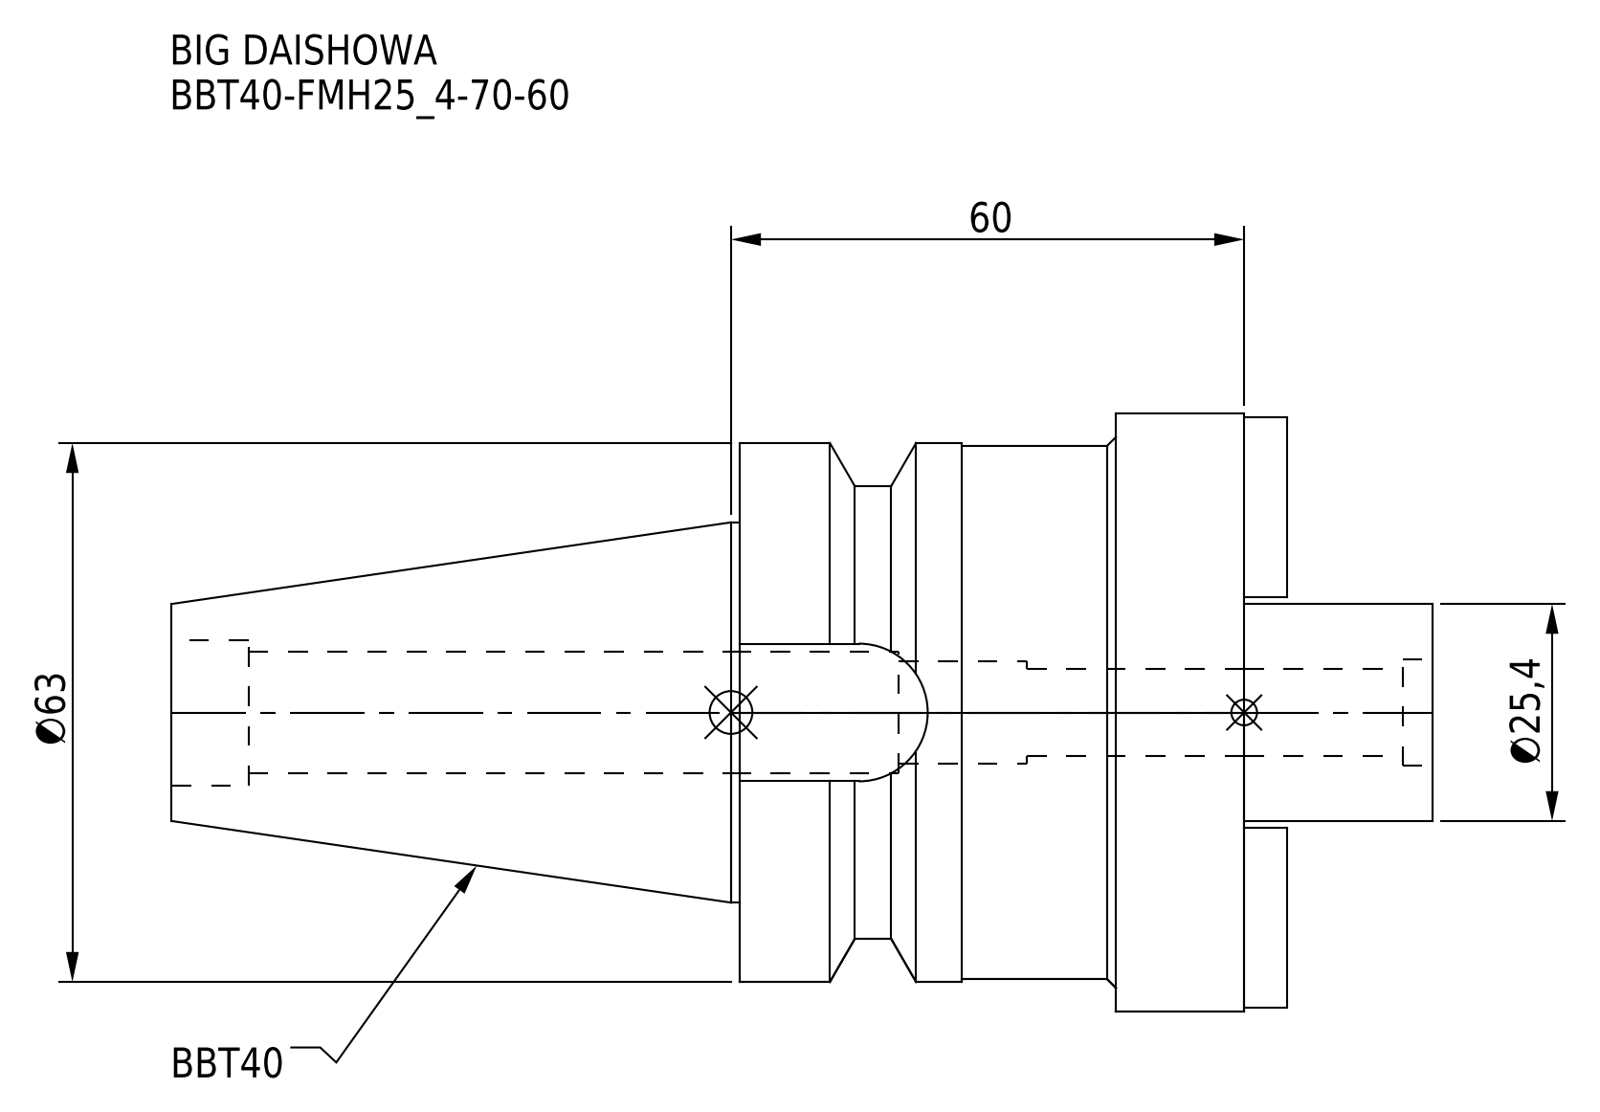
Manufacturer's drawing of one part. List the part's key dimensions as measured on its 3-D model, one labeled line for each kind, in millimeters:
Part name (STEP PRODUCT): BBT40-FMH25_4-70-60
STEP written by: CREO PARAMETRIC BY PTC INC, 2016380 (AUTOMOTIVE_DESIGN)
Units: millimetres
Bodies: 1 solid, 64 faces (26 planar, 30 cylindrical, 8 other)
Overall size (bounding box): 147.4 × 70 × 70
Volume: 241 767 mm³ · Surface area: 35 294 mm²
Round holes (diameter × count): ⌀10.25 ×1, ⌀12 ×1, ⌀12.5 ×1, ⌀14.2 ×1, ⌀17 ×1
Round bosses / shafts (diameter × count): ⌀70 ×1, ⌀63 ×1, ⌀62.4 ×1, ⌀53 ×1, ⌀44.45 ×1, ⌀25.4 ×1
Partial cylindrical surfaces — rounded edges, fillets, slot ends (radius × count): R8.05 ×1
Main face-to-face distances: 59, 15, 44, 17.75, 27.25, 5, 20, 64, 17, 22
